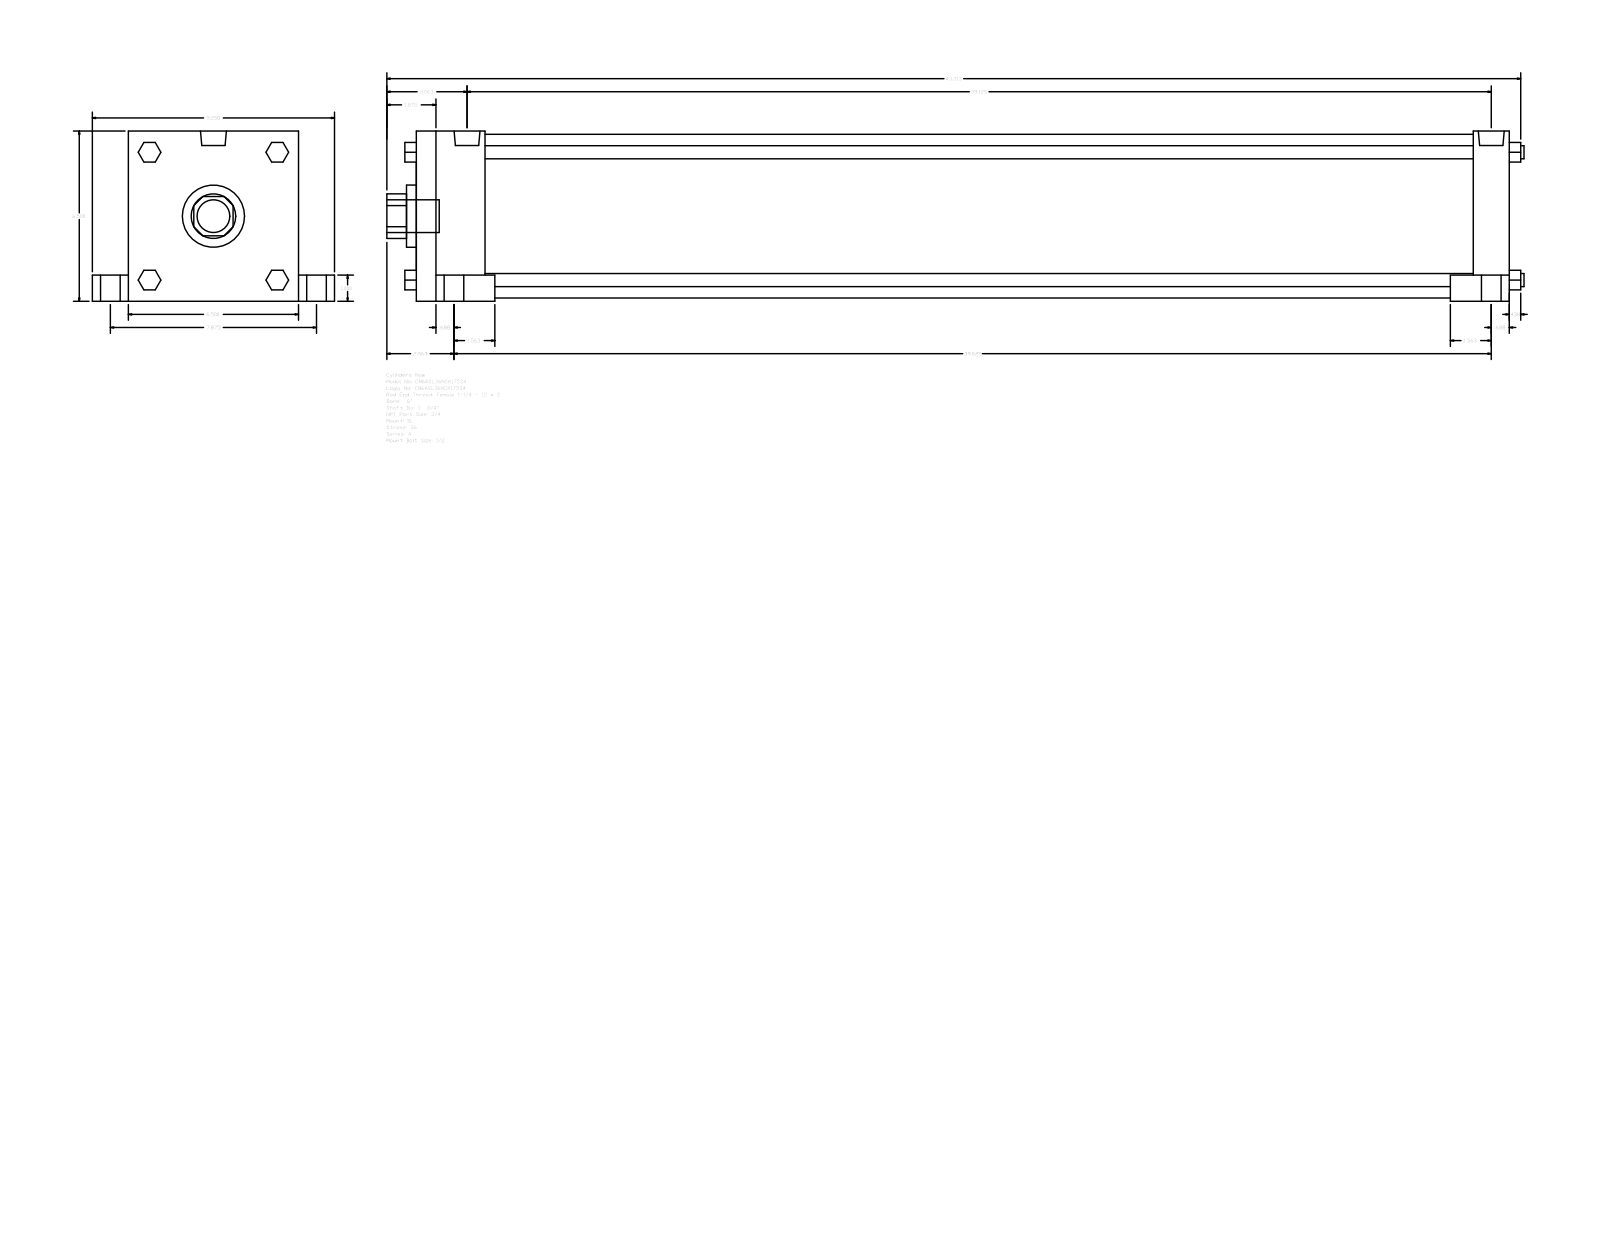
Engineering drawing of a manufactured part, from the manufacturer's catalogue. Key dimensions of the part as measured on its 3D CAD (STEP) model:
Part name (STEP PRODUCT): A_SL__0600_1.75
STEP written by: GSSL Pune (CONFIG_CONTROL_DESIGN)
Units: millimetres
Bodies: 0 solids, 150 faces (114 planar, 36 cylindrical, 0 other)
Overall size (bounding box): 1103.31 × 234.95 × 165.1
Round holes (diameter × count): ⌀44.45 ×1, ⌀60.33 ×1, ⌀158.75 ×1
Round bosses / shafts (diameter × count): ⌀25.4 ×4, ⌀19.05 ×4, ⌀15.08 ×4, ⌀12.7 ×4, ⌀25.12 ×2, ⌀31.75 ×1
Partial cylindrical surfaces — rounded edges, fillets, slot ends (radius × count): R21.63 ×1
Main face-to-face distances: 165.1, 1060.46, 66.68, 993.78, 1025.53, 958.85, 34.93, 34.92, 25.4, 139.7
